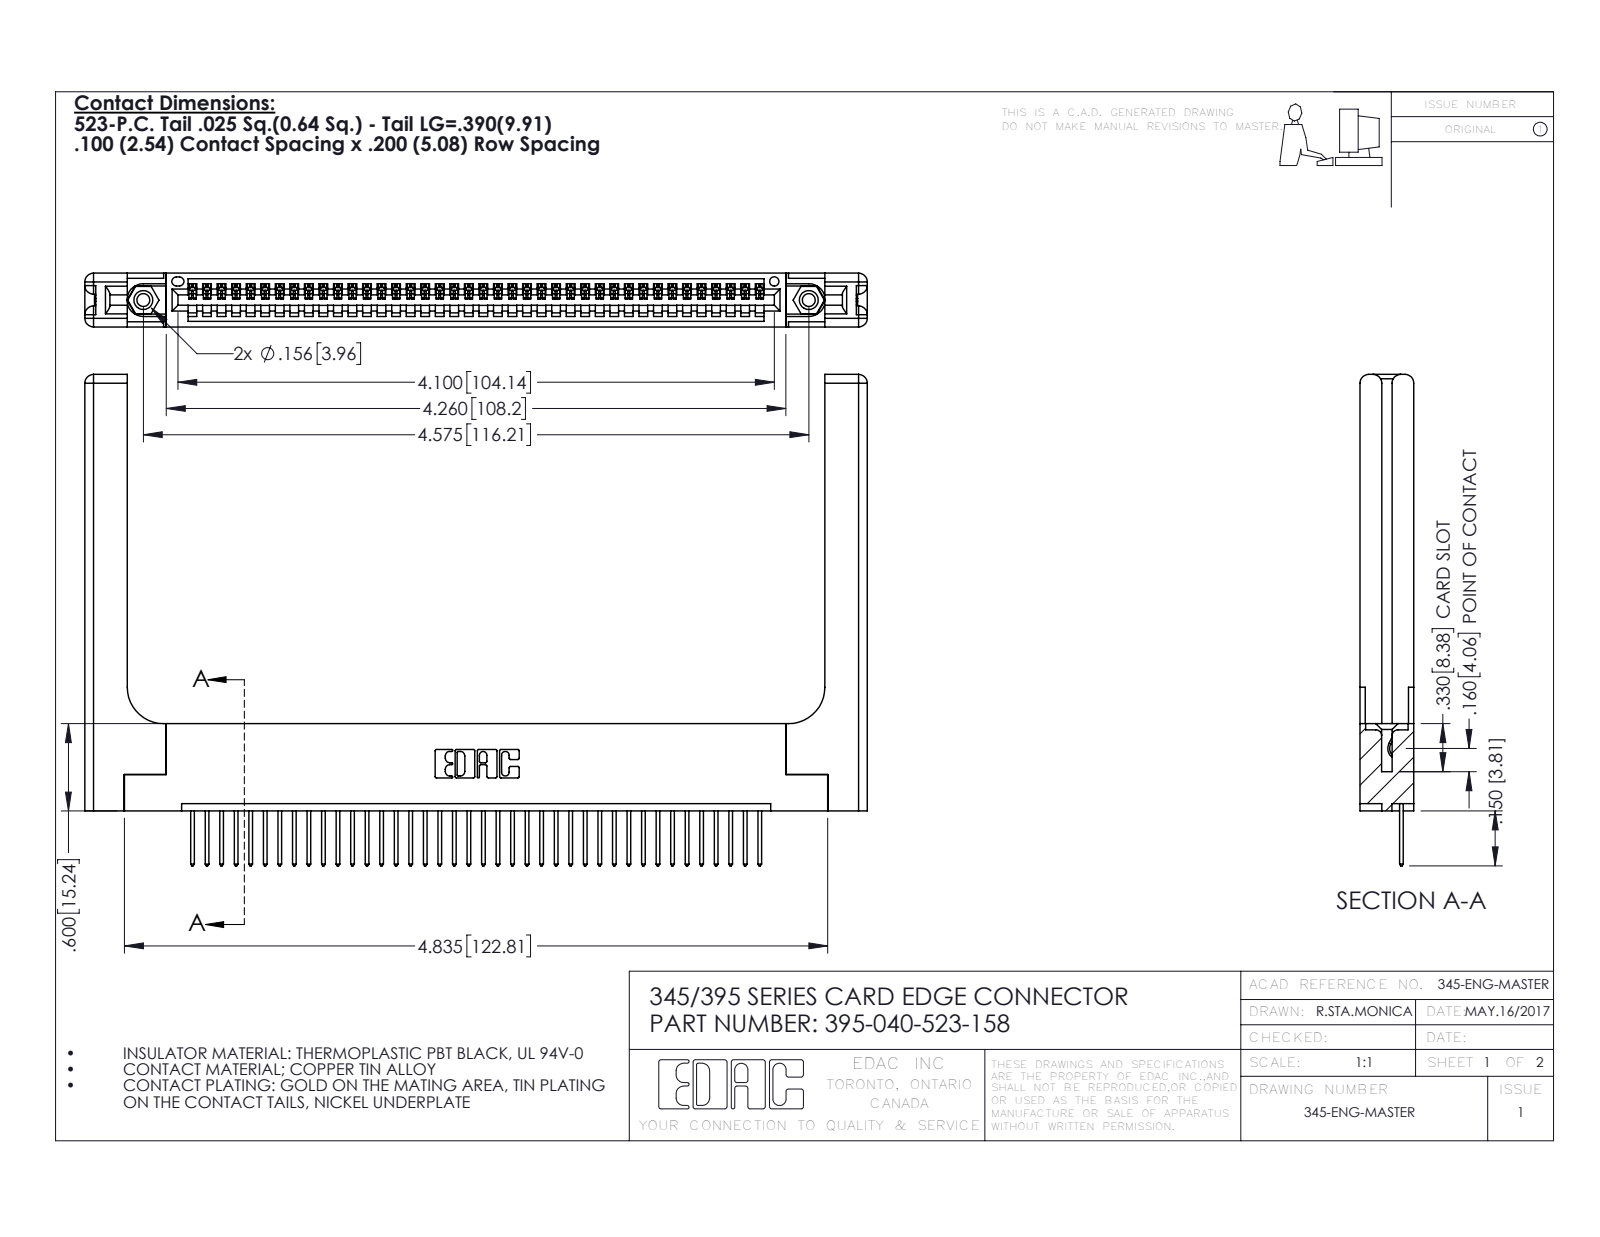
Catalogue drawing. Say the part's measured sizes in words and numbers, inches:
The part is named "345-292-001_345-293-123; 345-220-058_345-220-058; 395-040-523-158; 345-250-001_345-250-001-102 (+1 more)". Its 3-D file was written by "SolidWorks 2016 (CONFIG_CONTROL_DESIGN)". It is 45 solids with 2702 faces: 1828 planar, 814 cylindrical and 60 other. Overall it measures 5.379 by 3.377 by 0.37 inches. Its volume is 1.309 cubic inches and its surface area 34.91 square inches. Round holes: 2 of diameter 0.089, 2 of diameter 0.125, 2 of diameter 0.156, 1 of diameter 0.064. Round bosses or shafts: 2 of diameter 0.155. Partial cylindrical surfaces (rounded edges, fillets, slot ends): 80 of radius 0.006, 80 of radius 0.01, 22 of radius 0.01, 16 of radius 0.06, 6 of radius 0.007, 6 of radius 0.031, 3 of radius 0.026, 2 of radius 0.03. The main face-to-face distances are 0.072, 0.37, 0.298, 0.2, 0.098, 0.272, 0.025, 0.148, 0.15, 0.225. The hole center spacings are 0.27, 4.339, 4.575.
